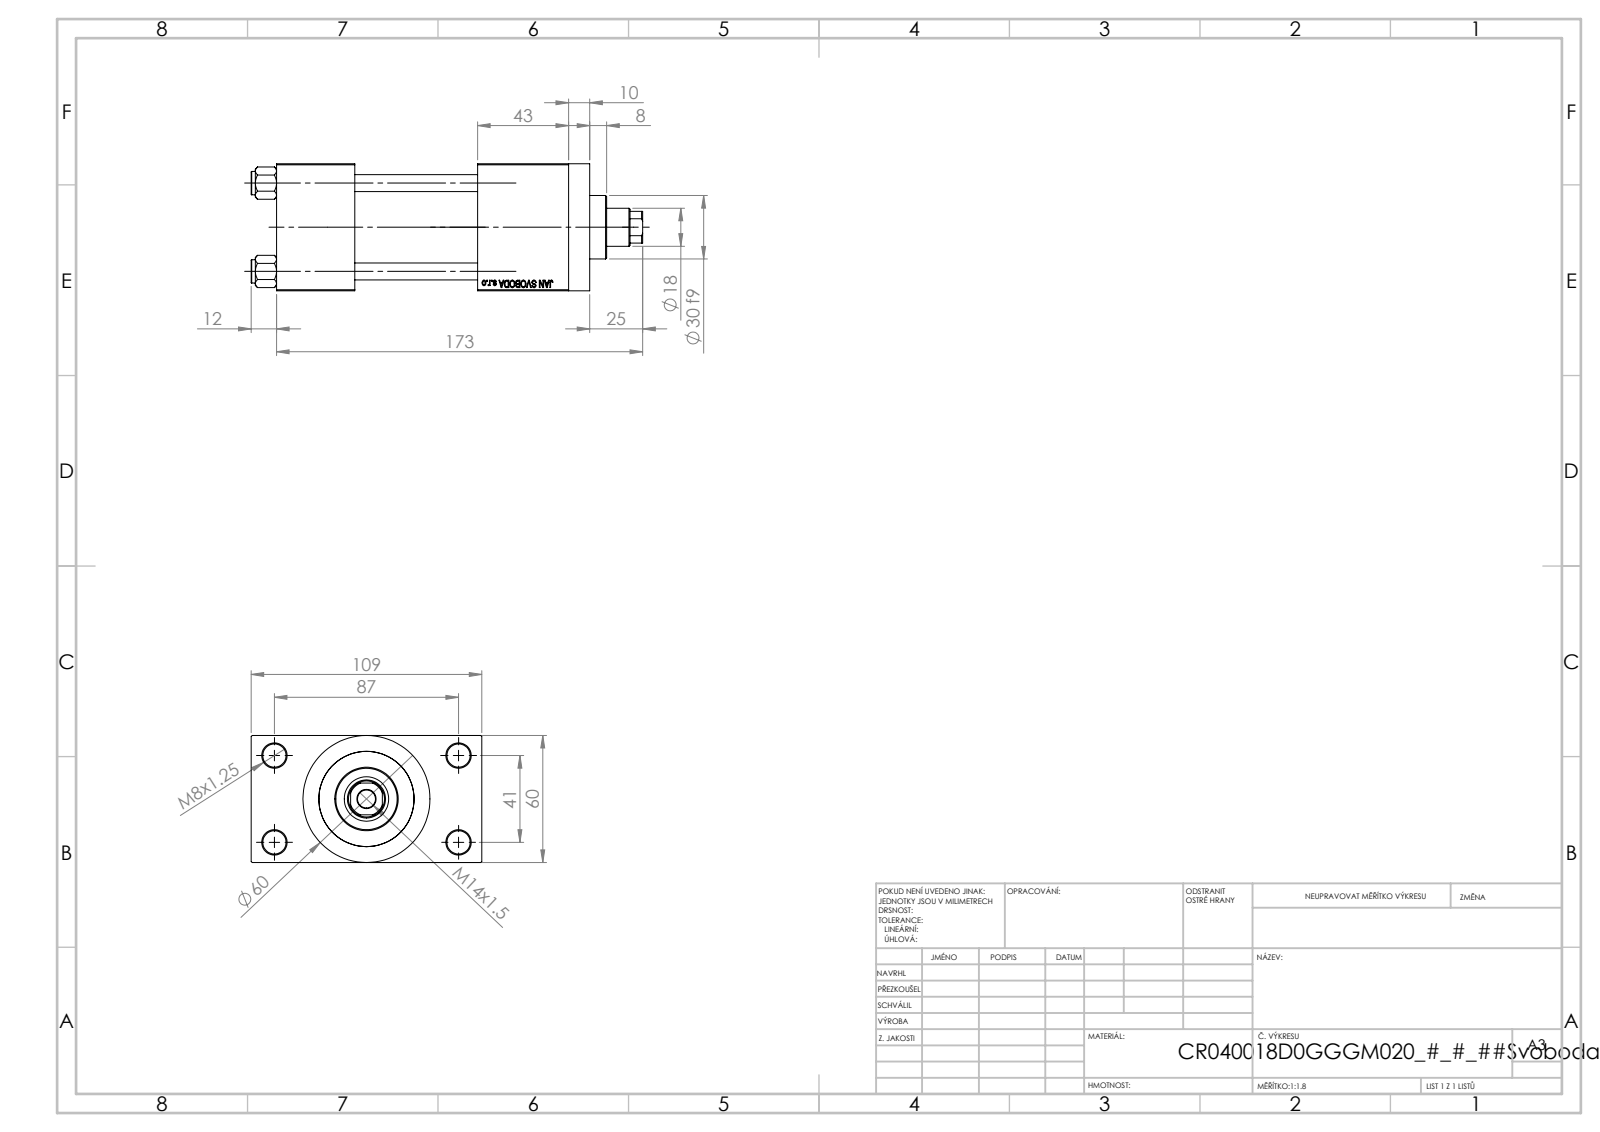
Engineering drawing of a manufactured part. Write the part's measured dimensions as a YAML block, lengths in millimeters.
part_name: "V215CR_D_TYCINKA; V215CR_D_Body; NUT_M5_D; V215CR_VCP_D (+1 more)"
step_written_by: "SolidWorks 2019 (CONFIG_CONTROL_DESIGN)"
units: millimeters
bodies: {solids: 11, faces: 1105, planar: 498, cylindrical: 89, other: 518}
overall_size: [185, 109, 60]
volume: 517766
surface_area: 121267
round_holes:
  - {diameter: 8, count: 4}
  - {diameter: 11, count: 4}
  - {diameter: 7, count: 2}
  - {diameter: 16.66, count: 2}
  - {diameter: 24, count: 2}
  - {diameter: 8.5, count: 1}
  - {diameter: 18, count: 1}
  - {diameter: 21, count: 1}
  - {diameter: 31, count: 1}
  - {diameter: 40, count: 1}
  - {diameter: 45, count: 1}
round_bosses_or_shafts:
  - {diameter: 11, count: 4}
  - {diameter: 60, count: 1}
  - {diameter: 46, count: 1}
  - {diameter: 30, count: 1}
partial_cylinders:
  - {radius: 8.5, count: 1}
face_to_face_distances: [60, 24.5, 84.5, 58, 37, 95, 138, 101, 43, 109]
hole_center_spacings: [22.65, 29.49, 41.7, 47.15, 48.09, 64.35, 76.49, 41]
